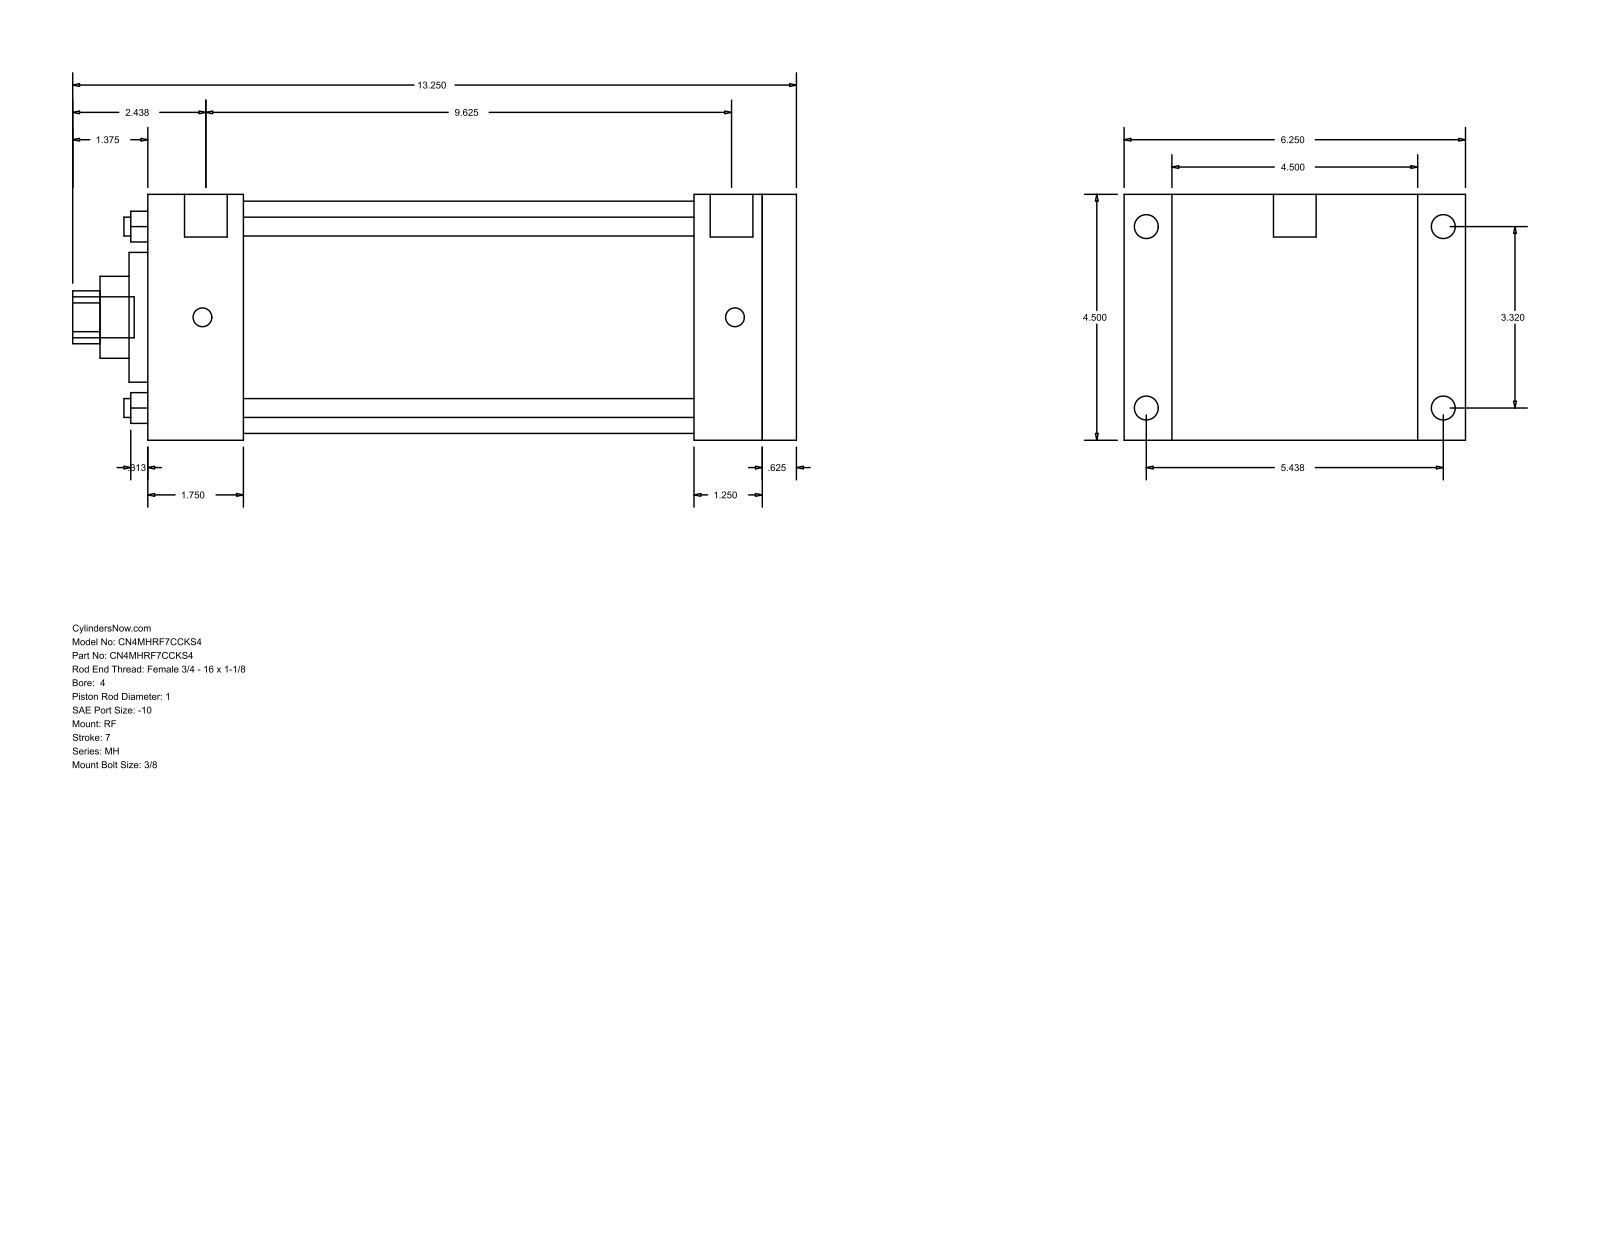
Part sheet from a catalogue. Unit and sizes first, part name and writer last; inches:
Units: inches
Overall size (bounding box): 13.25 × 6.25 × 4.5
Round holes (diameter × count): ⌀0.345 ×4, ⌀1 ×1, ⌀1.5 ×1, ⌀2.375 ×1, ⌀4.25 ×1
Round bosses / shafts (diameter × count): ⌀0.438 ×4, ⌀0.344 ×4, ⌀0.781 ×2, ⌀0.75 ×1
Partial cylindrical surfaces — rounded edges, fillets, slot ends (radius × count): R0.484 ×1
Main face-to-face distances: 4.5, 11.875, 0.625, 11.25, 1.75, 9.5, 10.125, 10, 8.25, 1.25
Hole centre spacings: 2.347, 3.32, 4.695
Bodies: 0 solids, 94 faces (65 planar, 29 cylindrical, 0 other)
Part name (STEP PRODUCT): MH_RF__0400_1
STEP written by: GSSL Pune (CONFIG_CONTROL_DESIGN)
